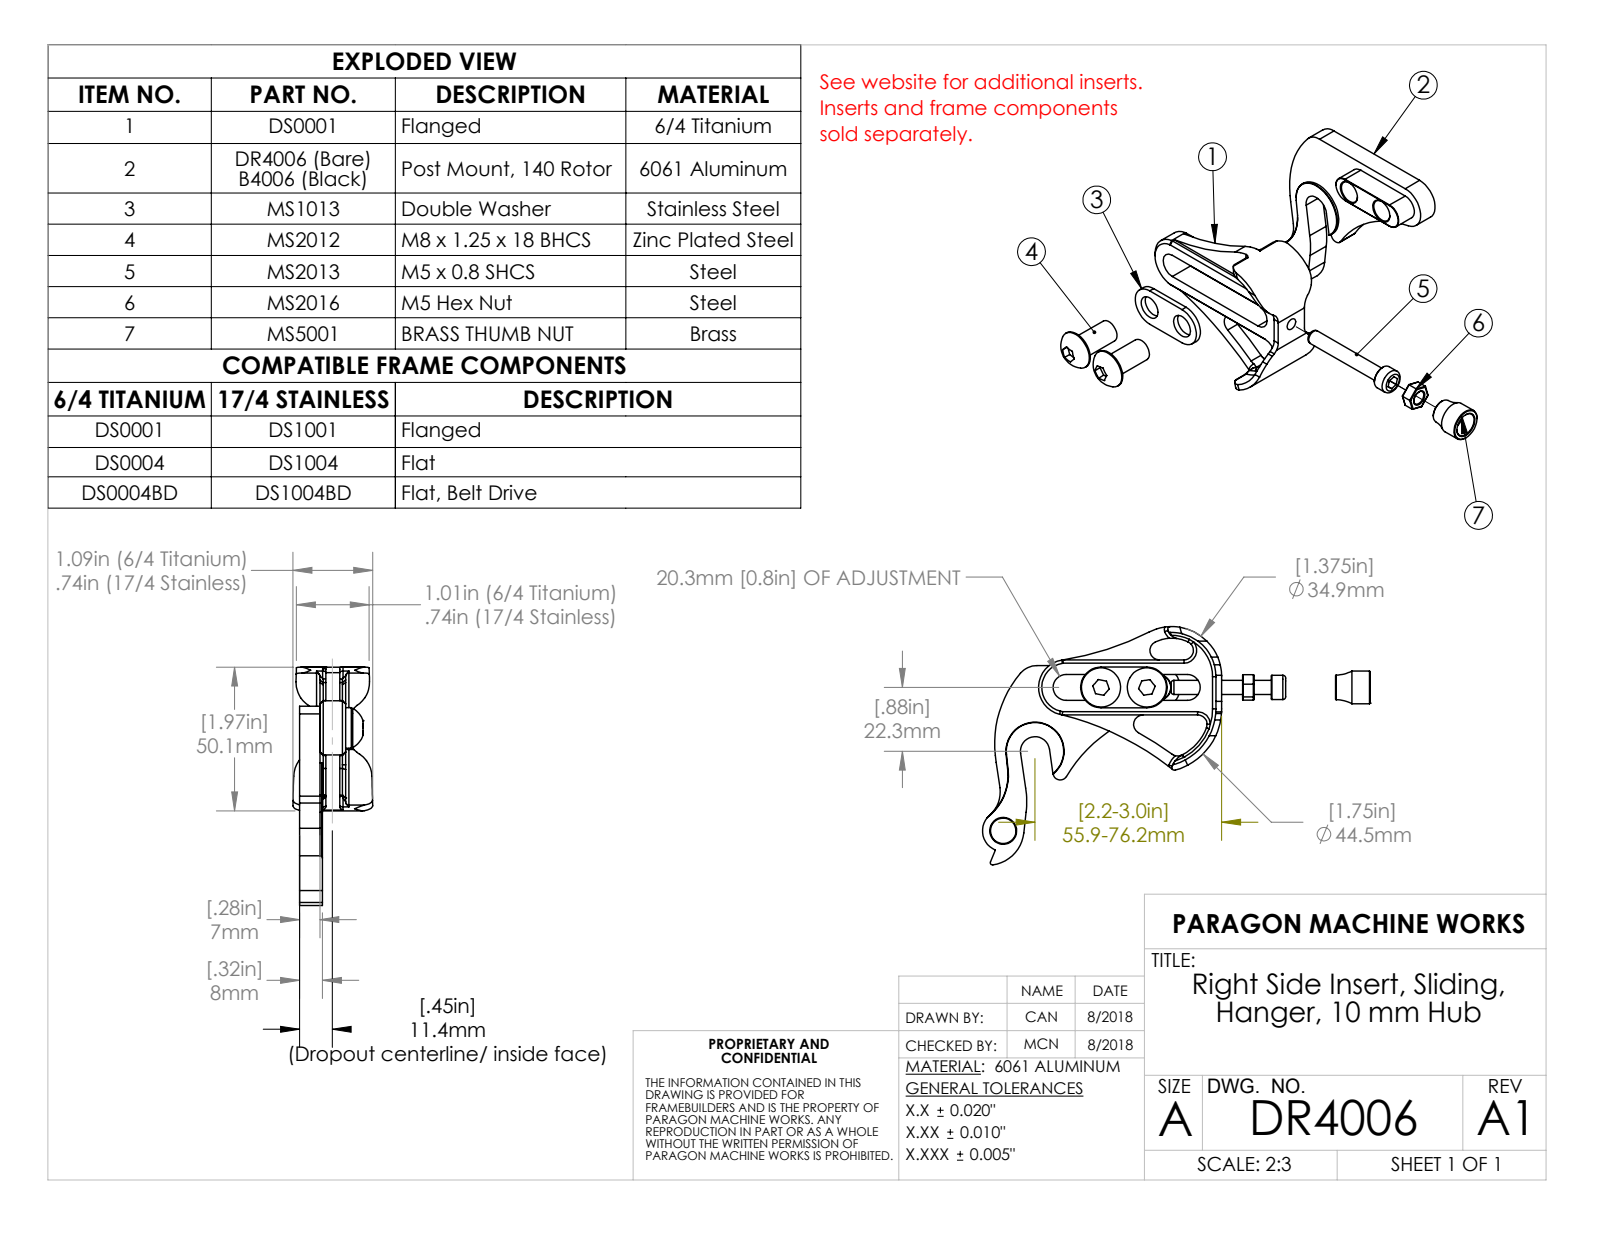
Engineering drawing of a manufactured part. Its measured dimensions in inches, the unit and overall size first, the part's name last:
Units: inches
Overall size (bounding box): 3.186 × 2.358 × 0.59
Round holes (diameter × count): ⌀0.312 ×2, ⌀0.35 ×1
Partial cylindrical surfaces — rounded edges, fillets, slot ends (radius × count): R0.178 ×2, R0.3 ×2, R0.03 ×1, R0.1 ×1, R0.2 ×1, R0.285 ×1, R0.4 ×1, R0.42 ×1
Main face-to-face distances: 0.28, 0.315, 0.035, 0.478, 0.356, 0.122, 0.59, 0.31, 0.275, 0.4
Hole centre spacings: 0.63, 2.387, 2.791
Volume: 0.863 in³ · Surface area: 10.9 in²
Bodies: 1 solid, 52 faces (17 planar, 24 cylindrical, 11 other)
Part name (STEP PRODUCT): DR4006
STEP written by: SolidWorks 2023 (AUTOMOTIVE_DESIGN)
